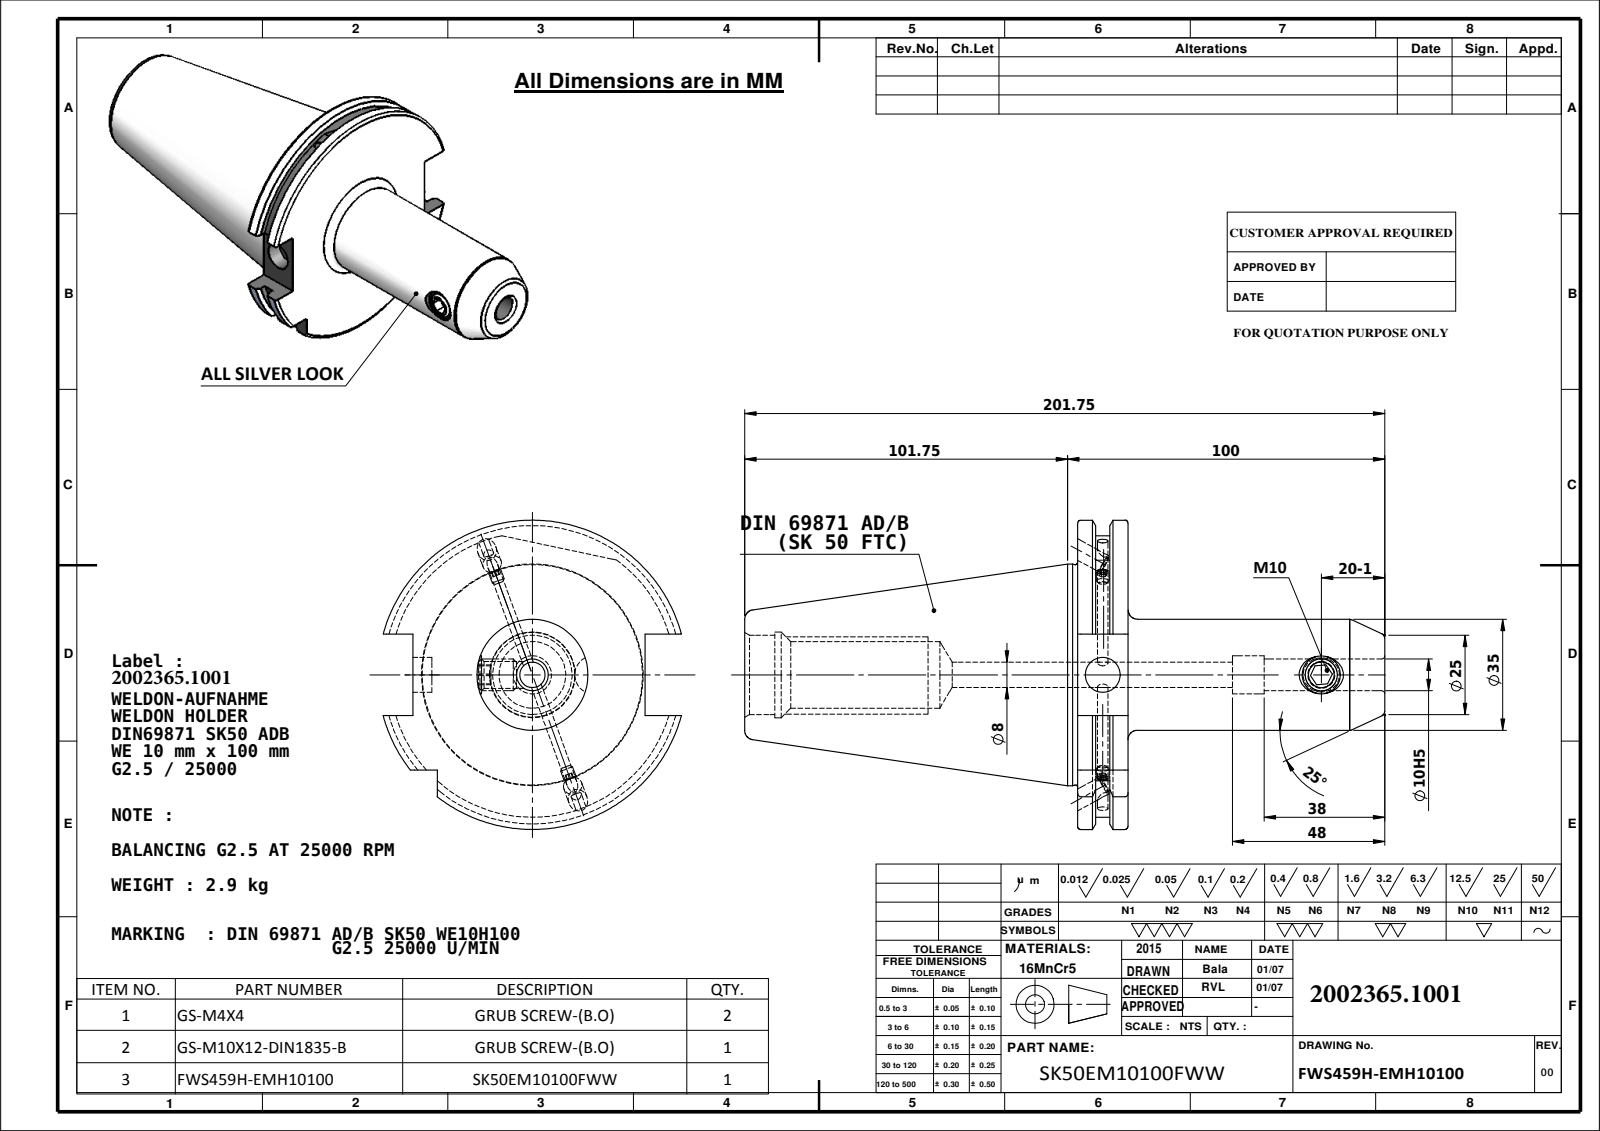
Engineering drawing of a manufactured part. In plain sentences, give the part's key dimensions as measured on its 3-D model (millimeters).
The part is named "91506-WE710100; SK50 EM 10 100 FTC WW; M10X12; Copy of M4X4_DIN 913 - M4 x 4-N". Its 3-D file was written by "SolidWorks 2009 (CONFIG_CONTROL_DESIGN)". It is 4 solids with 168 faces: 53 planar, 55 cylindrical and 60 other. Overall it measures 201.75 by 97.5 by 94.05 millimeters. Its volume is 404 103 cubic millimeters and its surface area 54 729 square millimeters. Round holes: 2 of diameter 6, 2 of diameter 12, 1 of diameter 3.3, 1 of diameter 8, 1 of diameter 8.5, 1 of diameter 10, 1 of diameter 11, 1 of diameter 21, 1 of diameter 25, 1 of diameter 27. Round bosses or shafts: 2 of diameter 4, 1 of diameter 69.85, 1 of diameter 69.45, 1 of diameter 35, 1 of diameter 10. Partial cylindrical surfaces (rounded edges, fillets, slot ends): 1 of radius 44.9, 1 of radius 48.75. The main face-to-face distances are 15.9, 5.66, 10.24, 10.15, 4.49, 5.75, 104.95, 110.61, 115.1, 120.85. The hole center spacings are 68.9.
